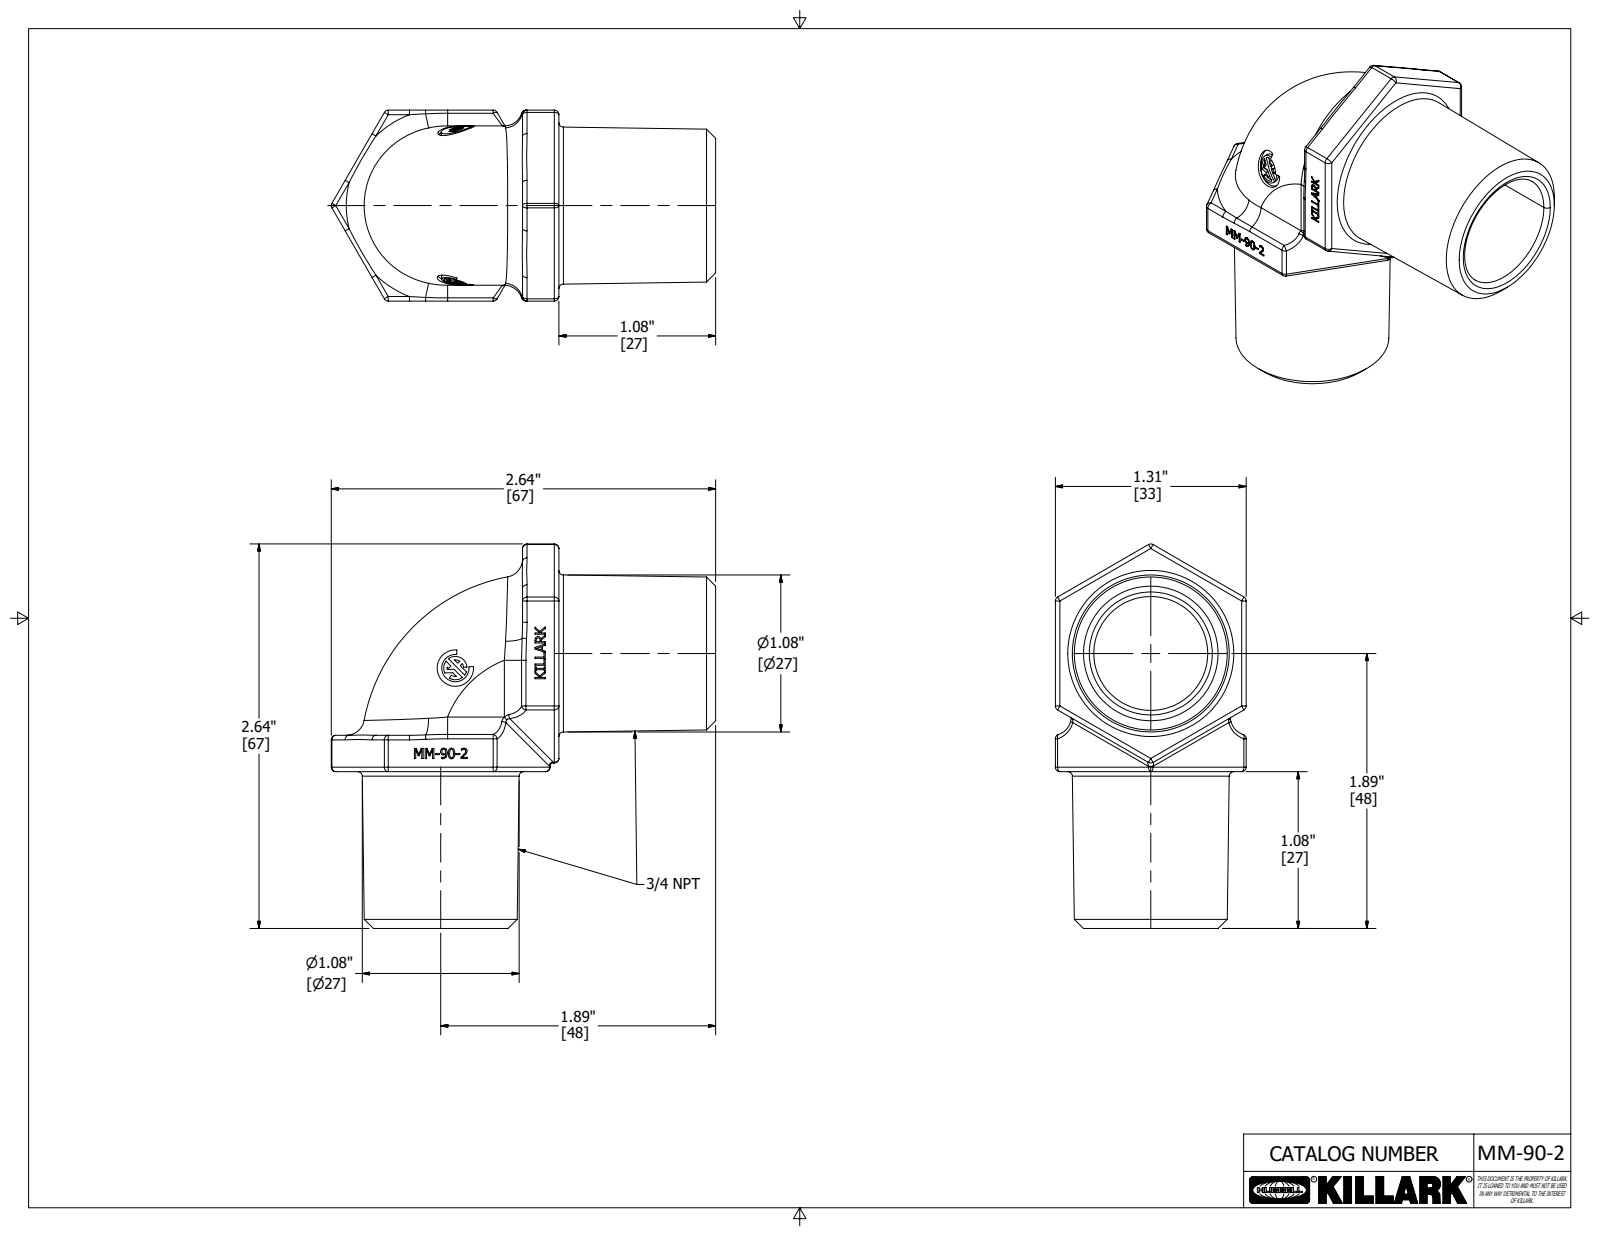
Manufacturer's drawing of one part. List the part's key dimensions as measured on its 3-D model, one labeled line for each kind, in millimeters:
Part name (STEP PRODUCT): MM-90-2
STEP written by: Autodesk Inventor 2020 (AUTOMOTIVE_DESIGN)
Units: millimetres
Bodies: 1 solid, 678 faces (376 planar, 60 cylindrical, 242 other)
Overall size (bounding box): 67.2 × 67.2 × 33.4
Volume: 29 200 mm³ · Surface area: 14 740 mm²
Round holes (diameter × count): ⌀6.4 ×1
Round bosses / shafts (diameter × count): ⌀5.2 ×1
Partial cylindrical surfaces — rounded edges, fillets, slot ends (radius × count): R0.8 ×38, R3.2 ×5, R0.2 ×1, R0.8 ×1, R1.4 ×1, R2 ×1, R2.4 ×1
Main face-to-face distances: 33.4, 27.4, 2.8, 30.6, 27.8, 6.4, 33.7, 0.5, 32.8, 2.3
